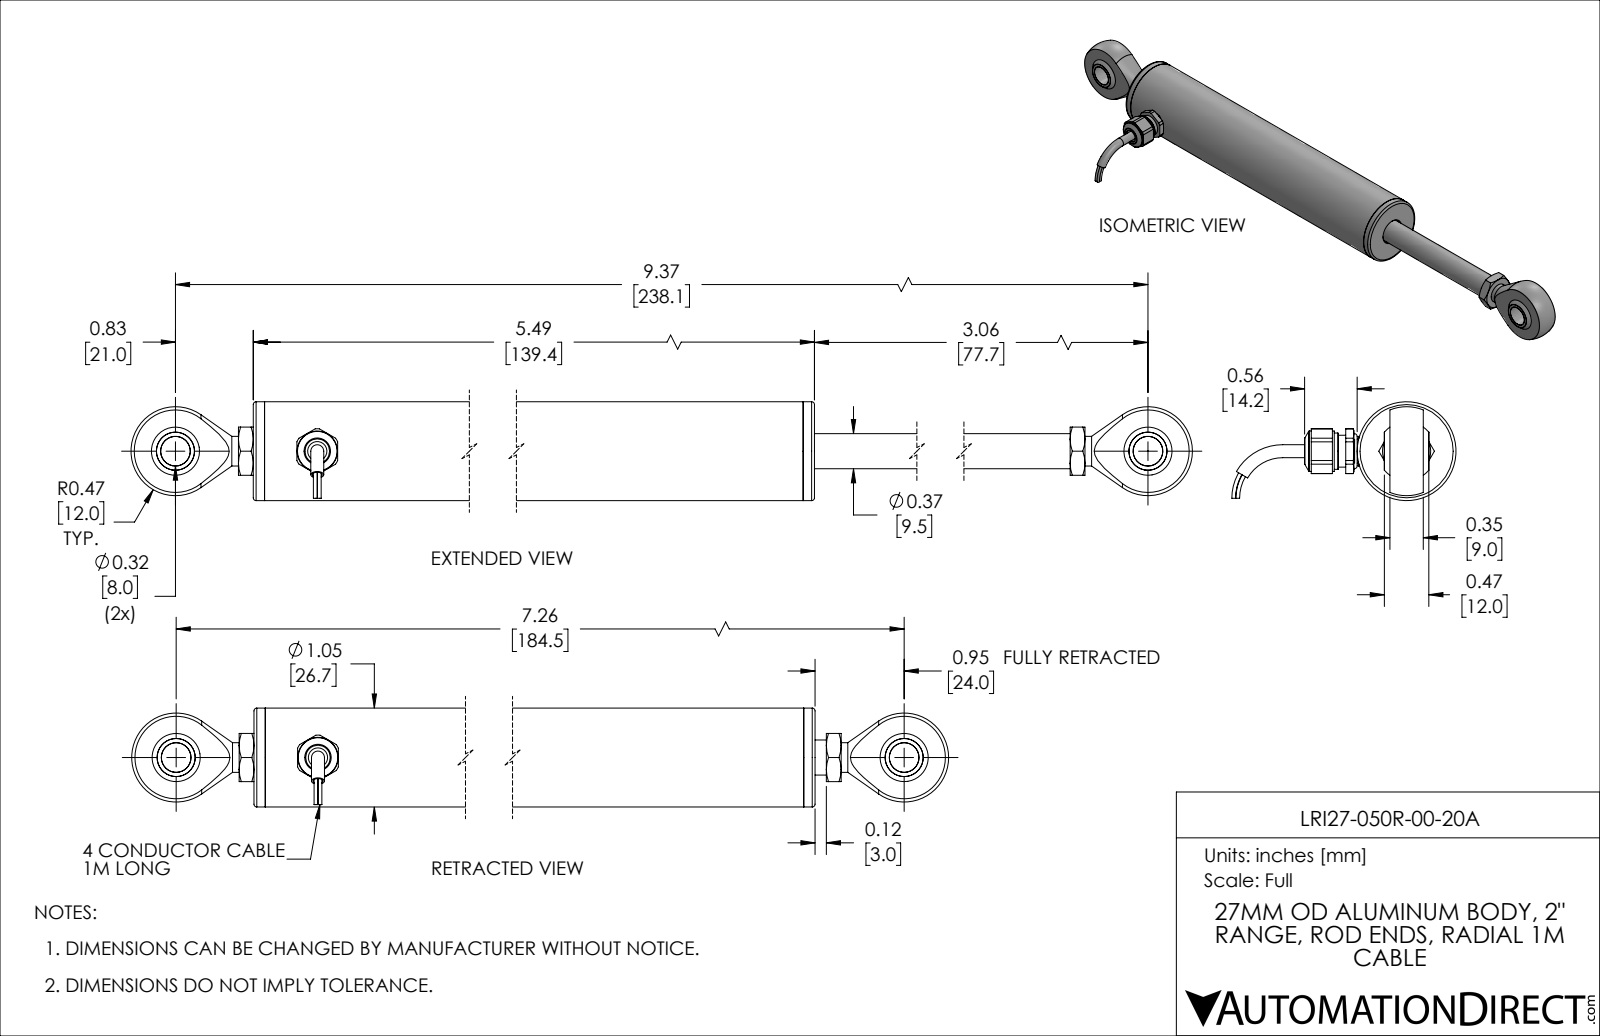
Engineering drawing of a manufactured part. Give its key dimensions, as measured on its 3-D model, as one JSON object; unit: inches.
{"part_name": "LRI27-050R-00-20A", "step_written_by": "SolidWorks 2019 (AUTOMOTIVE_DESIGN)", "units": "inches", "bodies": {"solids": 17, "faces": 219, "planar": 82, "cylindrical": 57, "other": 80}, "overall_size": [8.208, 2.382, 1.05], "volume_in3": 3.24, "surface_area_in2": 64.8, "round_holes": [[0.268, 2], [0.106, 1], [0.138, 1], [0.201, 1], [0.205, 1], [0.25, 1], [0.274, 1], [0.36, 1], [0.375, 1], [0.386, 1], [0.499, 1], [0.825, 1]], "round_bosses_or_shafts": [[0.315, 4], [0.039, 4], [1.05, 1], [0.848, 1], [0.5, 1], [0.429, 1], [0.386, 1], [0.373, 1]], "partial_cylinders_radius": [[0.238, 1]], "face_to_face_distances": [0.12, 5.37, 0.354, 5.49, 5.25, 0.4, 0.28, 4.97, 5.09, 0.157]}
